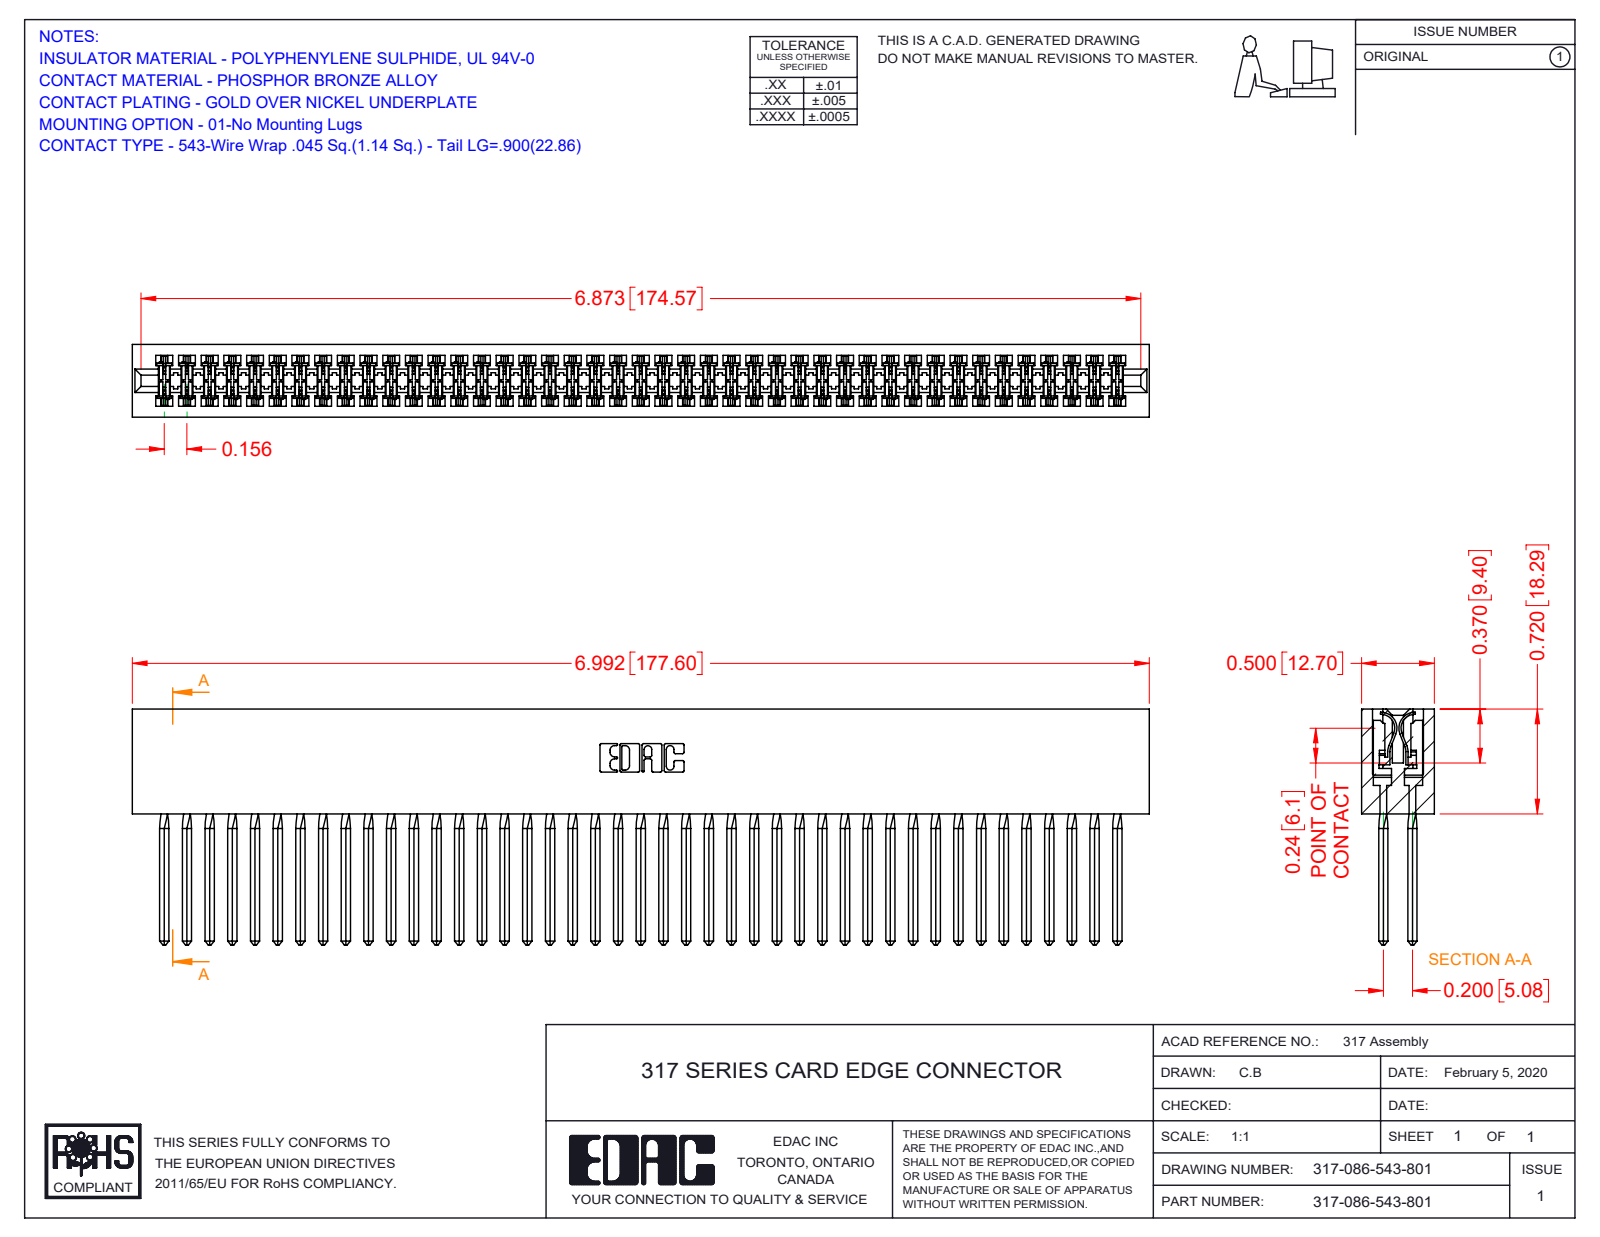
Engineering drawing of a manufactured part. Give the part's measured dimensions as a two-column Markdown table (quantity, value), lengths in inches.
| quantity | value |
| --- | --- |
| part name | 317 Part_Lugless; 317-086-543-801; 317-290-001_543 |
| STEP written by | SolidWorks 2016 (CONFIG_CONTROL_DESIGN) |
| units | inches |
| bodies | 87 solids, 7744 faces (6328 planar, 1072 cylindrical, 344 other) |
| overall size | 6.992 × 1.62 × 0.5 |
| volume | 1.957 in³ |
| surface area | 75.88 in² |
| partial cylindrical surfaces (radius × count) | 0.015 × 172, 0.01 × 22, 0.007 × 6, 0.031 × 6, 0.026 × 3, 0.095 × 2, 0.1 × 2, 0.11 × 2 |
| main face-to-face distances | 0.075, 0.5, 0.425, 0.35, 0.195, 0.11, 0.094, 0.2, 0.115, 0.131 |
